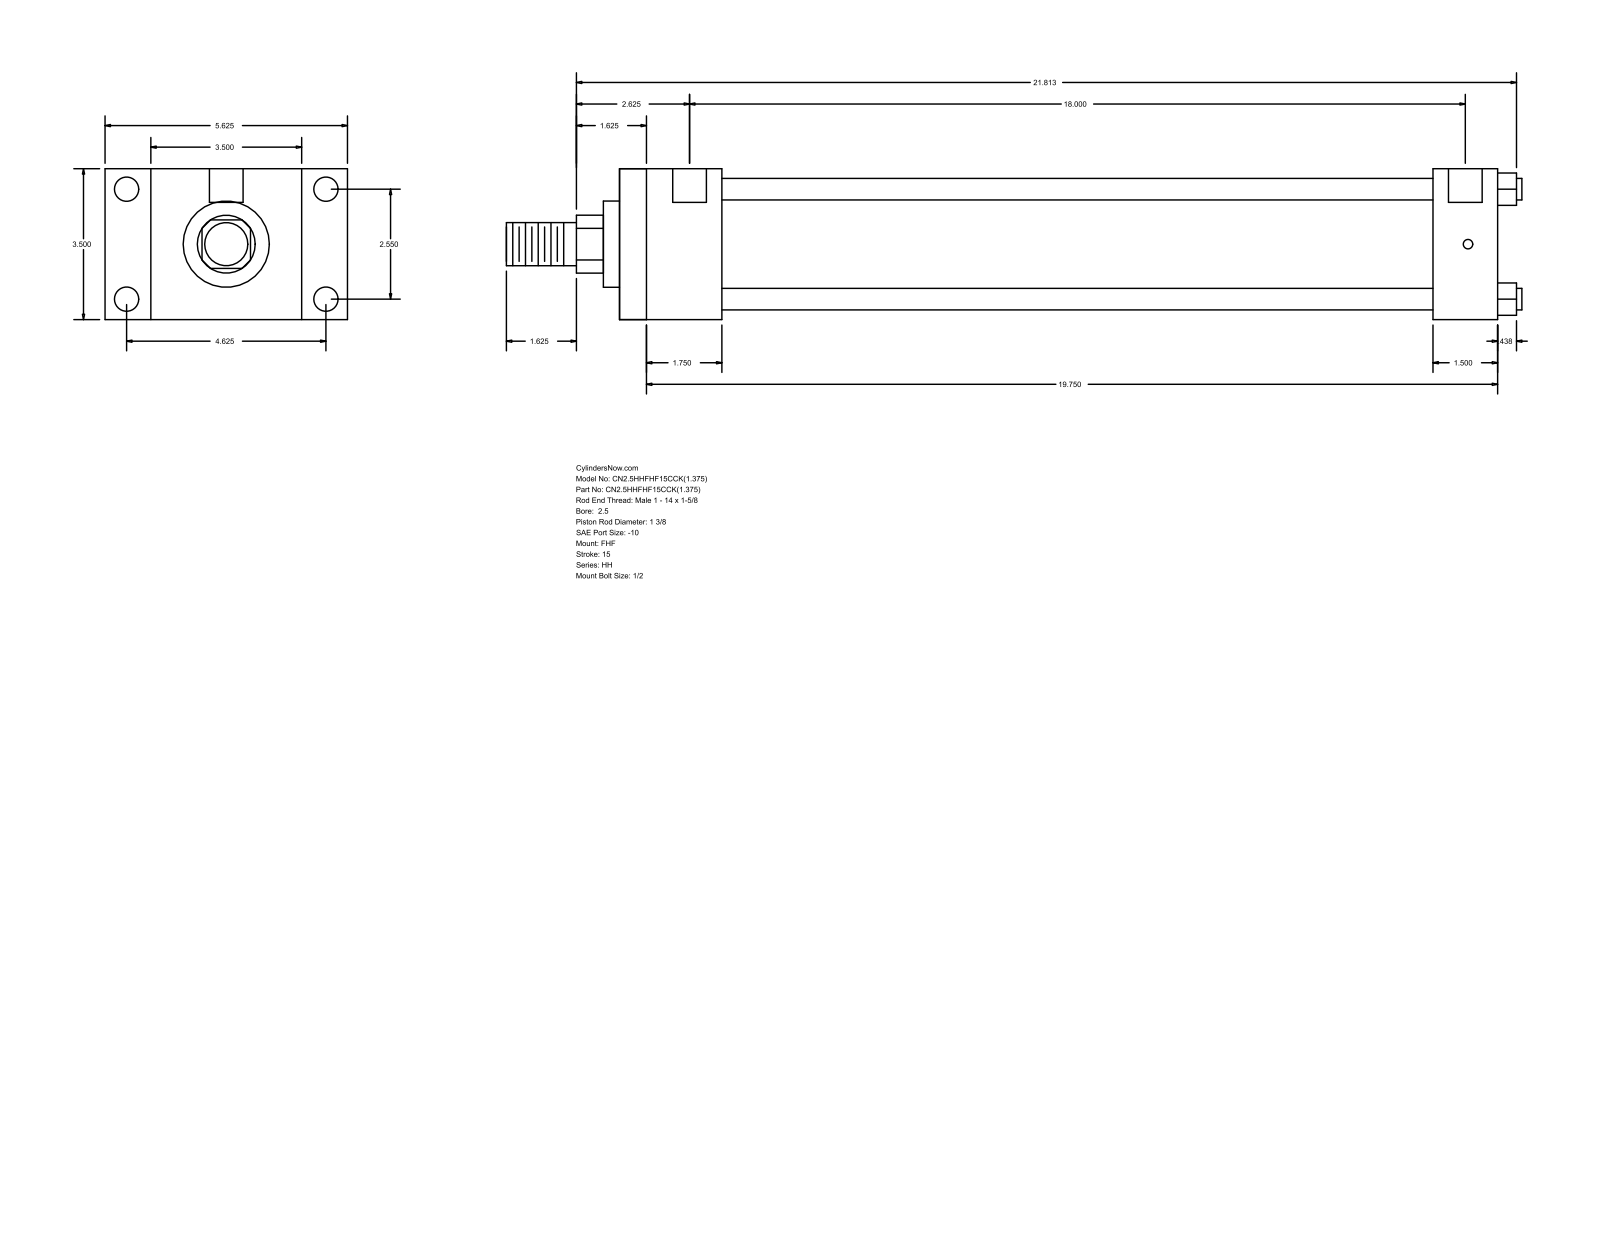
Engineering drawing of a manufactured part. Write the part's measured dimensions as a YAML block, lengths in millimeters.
part_name: "HH_FHF__0250_1.375"
step_written_by: "GSSL Pune (CONFIG_CONTROL_DESIGN)"
units: millimeters
bodies: {solids: 0, faces: 88, planar: 60, cylindrical: 28, other: 0}
overall_size: [598.49, 142.88, 88.9]
round_holes:
  - {diameter: 5.56, count: 4}
  - {diameter: 14.3, count: 4}
  - {diameter: 19.84, count: 2}
round_bosses_or_shafts:
  - {diameter: 12.7, count: 4}
  - {diameter: 73.03, count: 1}
  - {diameter: 50.8, count: 1}
  - {diameter: 34.92, count: 1}
  - {diameter: 25.4, count: 1}
partial_cylinders:
  - {radius: 17.06, count: 1}
face_to_face_distances: [88.9, 60.32, 26.99, 115.89, 517.52, 457.2, 142.88, 479.42, 419.1, 38.1]
hole_center_spacings: [1.58, 64.76, 117.48, 134.15, 458.79, 460.37, 457.21]
